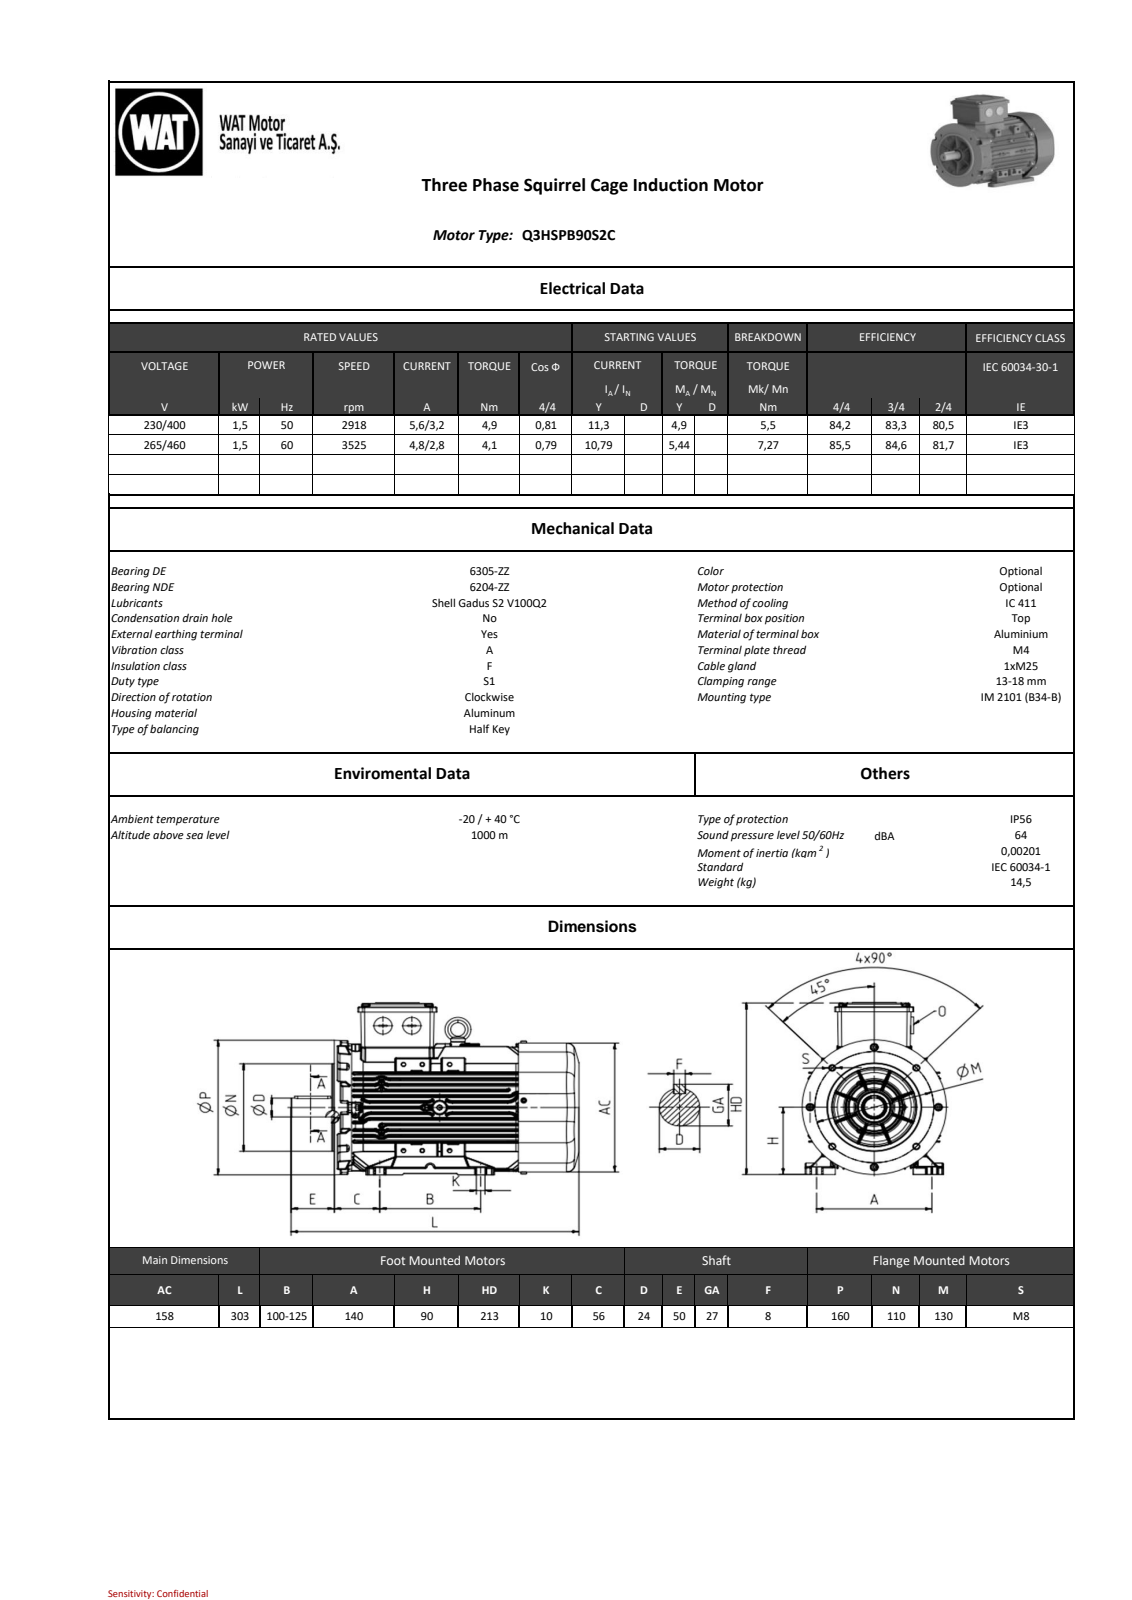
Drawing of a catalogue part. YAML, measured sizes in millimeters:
part_name: "Ar311A3C0609zrjw"
step_written_by: "SIEMENS PLM Software NX 9.0 (AUTOMOTIVE_DESIGN)"
units: millimeters
bodies: {solids: 0, faces: 9432, planar: 1852, cylindrical: 2926, other: 4654}
overall_size: [303, 211.5, 162.94]
round_holes:
  - {diameter: 6.8, count: 5}
  - {diameter: 4.92, count: 4}
  - {diameter: 6.4, count: 4}
  - {diameter: 3, count: 3}
  - {diameter: 4.13, count: 3}
  - {diameter: 4.6, count: 2}
  - {diameter: 5.1, count: 2}
  - {diameter: 0.24, count: 1}
  - {diameter: 3.5, count: 1}
  - {diameter: 3.99, count: 1}
  - {diameter: 8, count: 1}
  - {diameter: 8.4, count: 1}
round_bosses_or_shafts:
  - {diameter: 6, count: 12}
  - {diameter: 11.6, count: 4}
  - {diameter: 10, count: 4}
  - {diameter: 9.3, count: 4}
  - {diameter: 8.33, count: 4}
  - {diameter: 9.2, count: 2}
  - {diameter: 5, count: 2}
  - {diameter: 146.5, count: 1}
partial_cylinders:
  - {radius: 0.5, count: 1297}
  - {radius: 0.8, count: 342}
  - {radius: 1, count: 203}
  - {radius: 0.7, count: 40}
  - {radius: 2, count: 23}
  - {radius: 4, count: 15}
  - {radius: 0.1, count: 12}
  - {radius: 5, count: 11}
face_to_face_distances: [1, 138, 169, 6, 31, 4, 39.5, 153, 40.5, 41.96]
hole_center_spacings: [25.5, 65, 91.92, 21.04, 74.79, 85.12, 111.32, 138.54]
